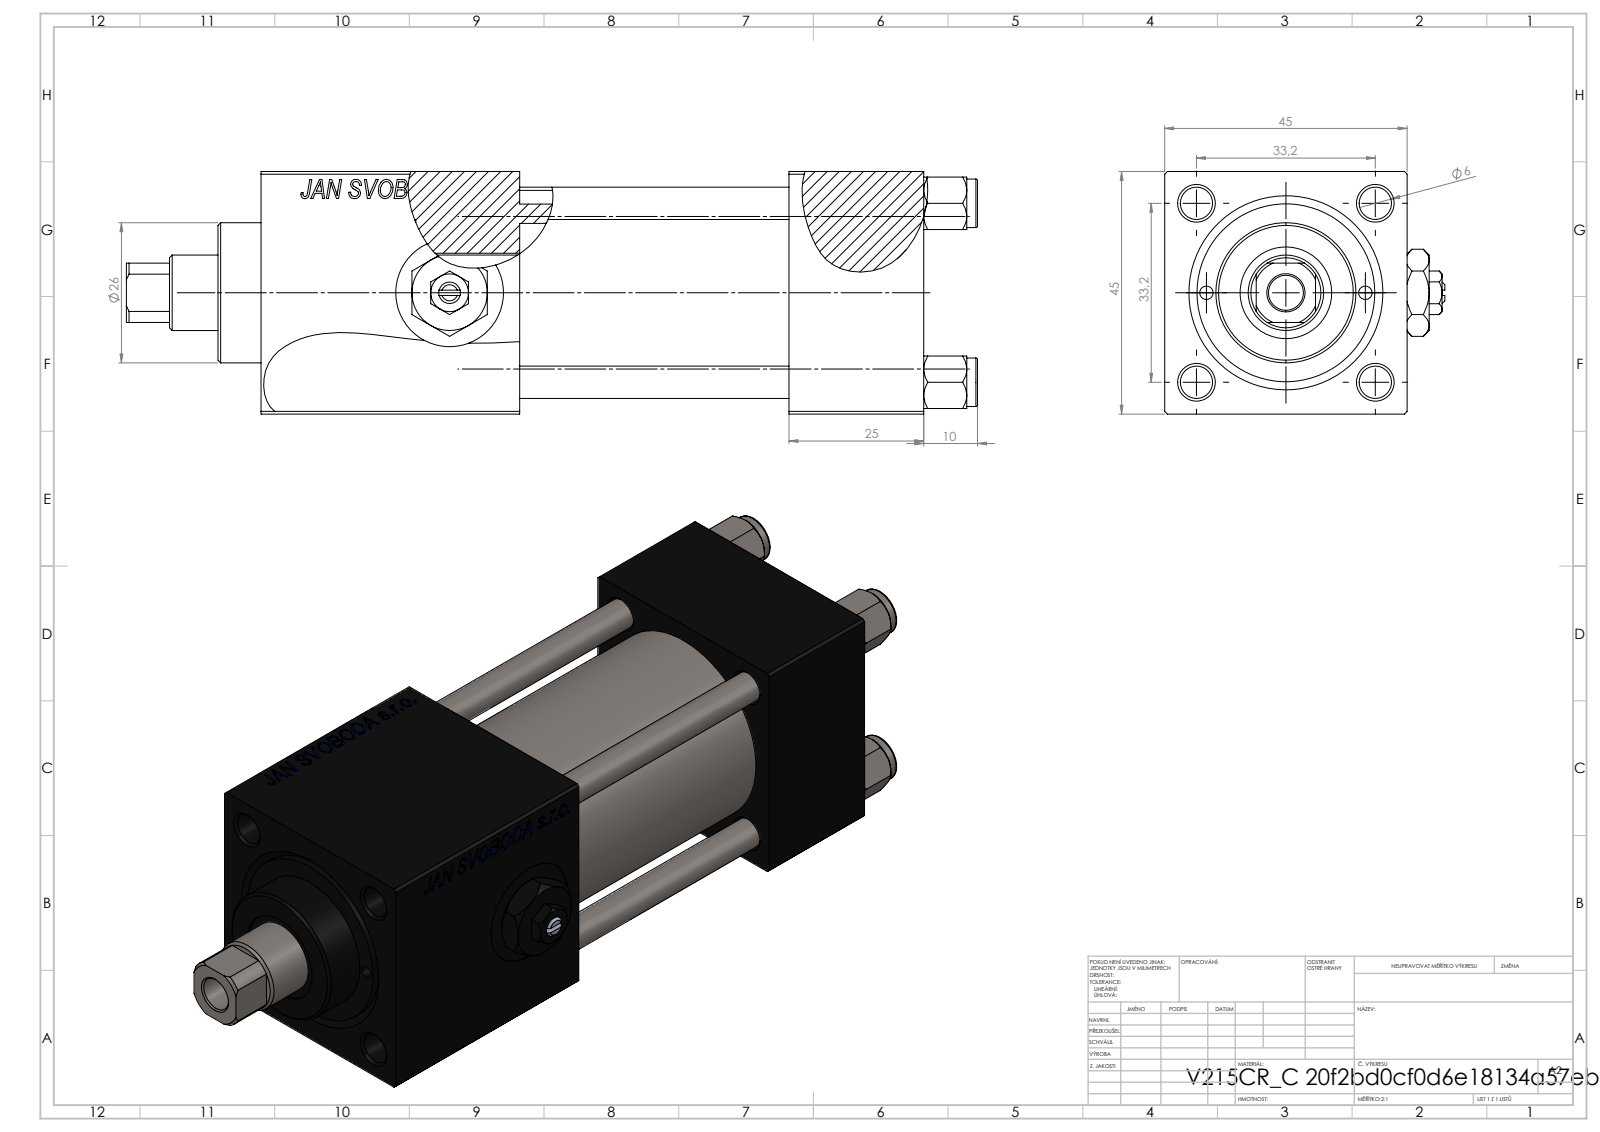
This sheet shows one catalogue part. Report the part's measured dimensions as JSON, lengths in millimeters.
{"part_name": "V215CR_C_TYCINKA; Zatka_pro_OIL_PORT; V215_VC_A; V215CR_VCP_C (+2 more)", "step_written_by": "SolidWorks 2019 (CONFIG_CONTROL_DESIGN)", "units": "millimeters", "bodies": {"solids": 12, "faces": 1201, "planar": 551, "cylindrical": 94, "other": 556}, "overall_size": [158, 52, 45], "volume_mm3": 193143, "surface_area_mm2": 67925, "round_holes": [[6, 4], [2.5, 2], [7, 2], [13.16, 2], [20, 2], [6.5, 1], [14, 1], [17, 1], [24, 1], [32, 1], [33, 1]], "round_bosses_or_shafts": [[9, 4], [38, 1], [26, 1]], "partial_cylinders_radius": [[6.5, 1]], "face_to_face_distances": [45, 25, 98, 123, 50, 75, 48, 94.3, 69.3, 19.3], "hole_center_spacings": [16.7, 23.48, 33.2, 35.47, 14.75, 46.95, 29.5, 75.5]}
